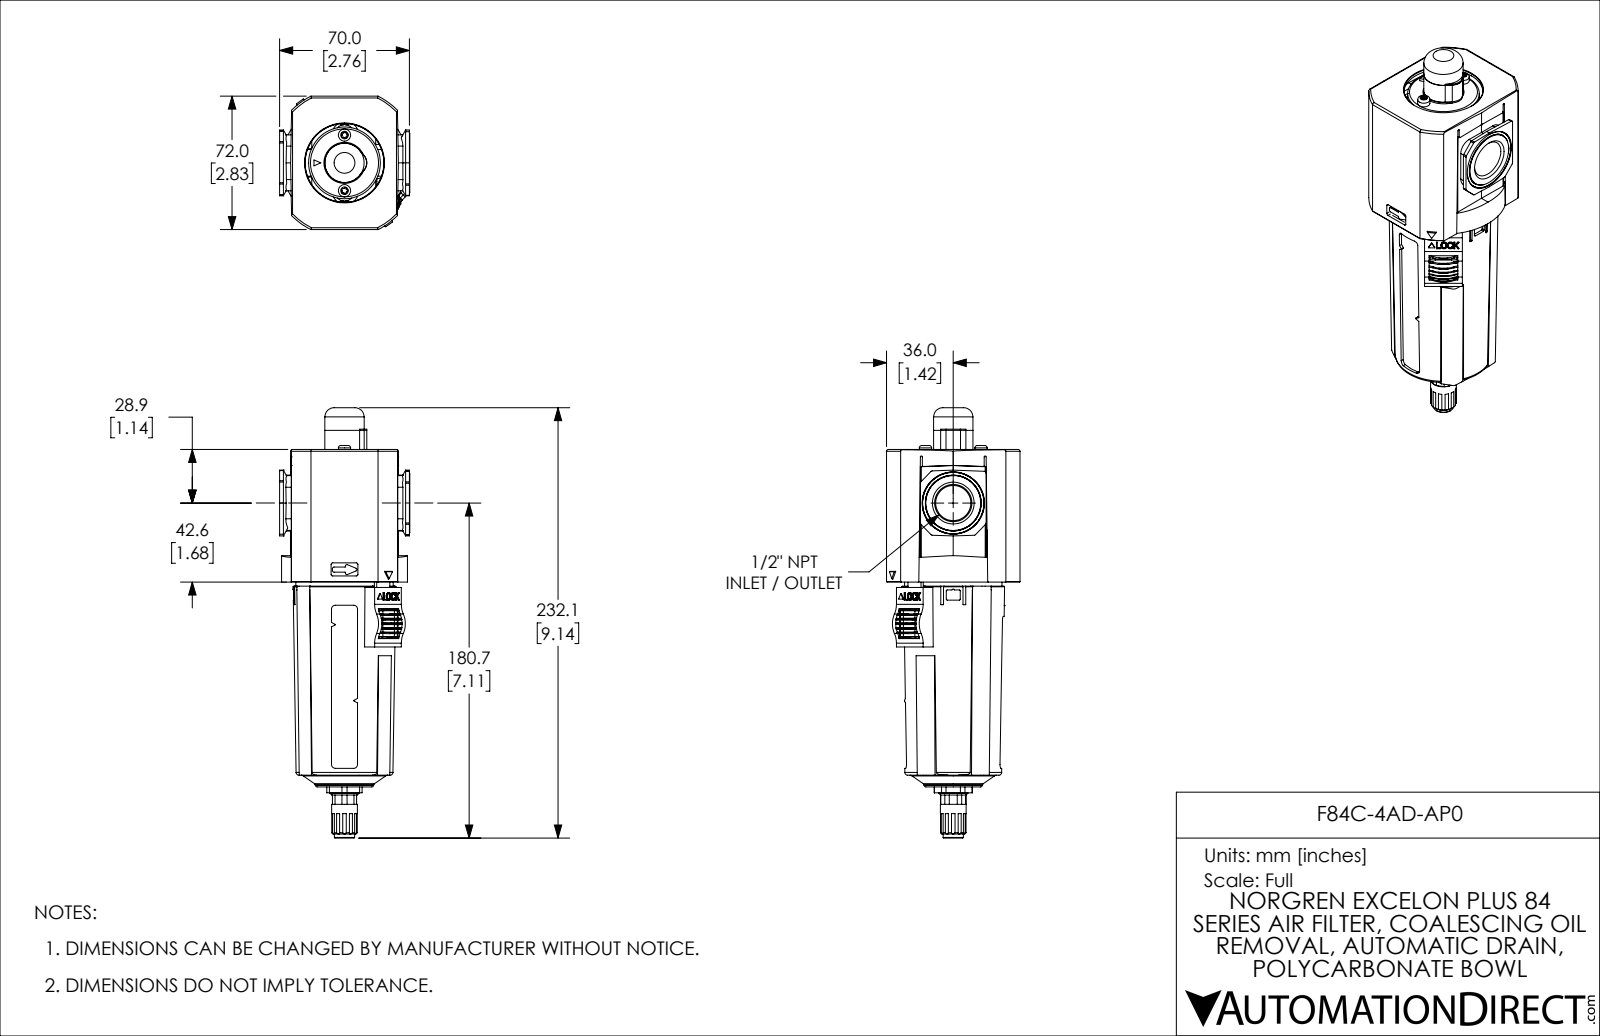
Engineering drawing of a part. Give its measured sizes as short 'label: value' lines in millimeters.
name: F84C-4AD-AP0
written by: SolidWorks 2021 (CONFIG_CONTROL_DESIGN)
unit: mm
bodies: 7 solids, 1207 faces (546 planar, 467 cylindrical, 194 other)
size: 232.1 × 72 × 70.3
volume: 474 700 mm³; area: 101 000 mm²
holes: 2× ⌀4.1, 2× ⌀4.5, 1× ⌀5.6, 1× ⌀6.2, 1× ⌀19.7, 1× ⌀24.6, 1× ⌀62.5
bosses: 2× ⌀8, 2× ⌀7, 2× ⌀6.6, 1× ⌀38.7, 1× ⌀25.4, 1× ⌀24.6, 1× ⌀23, 1× ⌀21.2
rounds: 60× R0.5, 44× R1, 24× R0.3, 16× R0.7, 10× R0.2, 8× R1, 8× R1.1, 8× R1.5
face distances: 72, 61.2, 1.5, 0.9, 60.4, 49.6, 48.6, 11.7, 70, 59.7
hole spacings: 15, 15.1, 30.1, 30, 30.2
